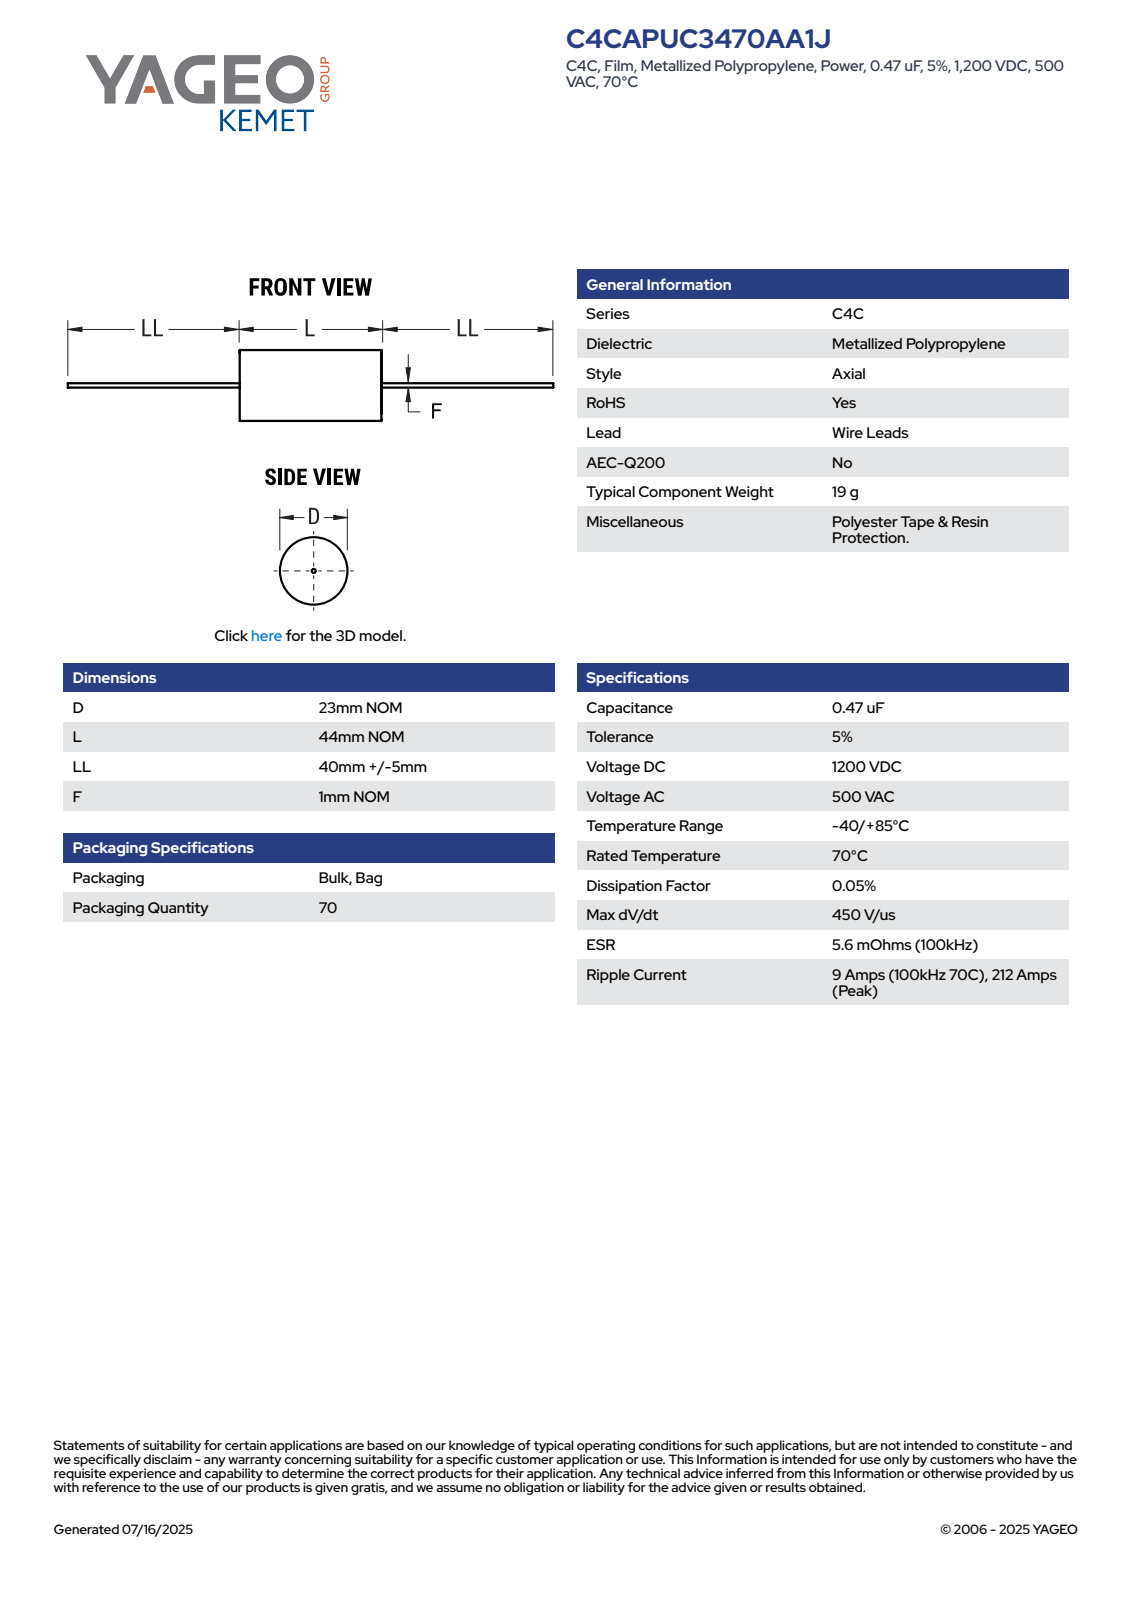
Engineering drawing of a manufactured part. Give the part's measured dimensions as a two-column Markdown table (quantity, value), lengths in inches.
| quantity | value |
| --- | --- |
| part name | CFP_ACWF_23X44_D23L44LL45F1 |
| STEP written by | SolidWorks 2014 (AUTOMOTIVE_DESIGN) |
| units | inches |
| bodies | 2 solids, 87 faces (28 planar, 28 cylindrical, 31 other) |
| overall size | 5.276 × 0.906 × 0.906 |
| volume | 1.12 in³ |
| surface area | 7.941 in² |
| round bosses / shafts (diameter × count) | 0.906 × 1, 0.039 × 1 |
| partial cylindrical surfaces (radius × count) | 0.452 × 1 |
| main face-to-face distances | 1.732, 1.732, 1.771, 1.772, 3.504, 5.276, 3.504, 3.504, 1.772 |
